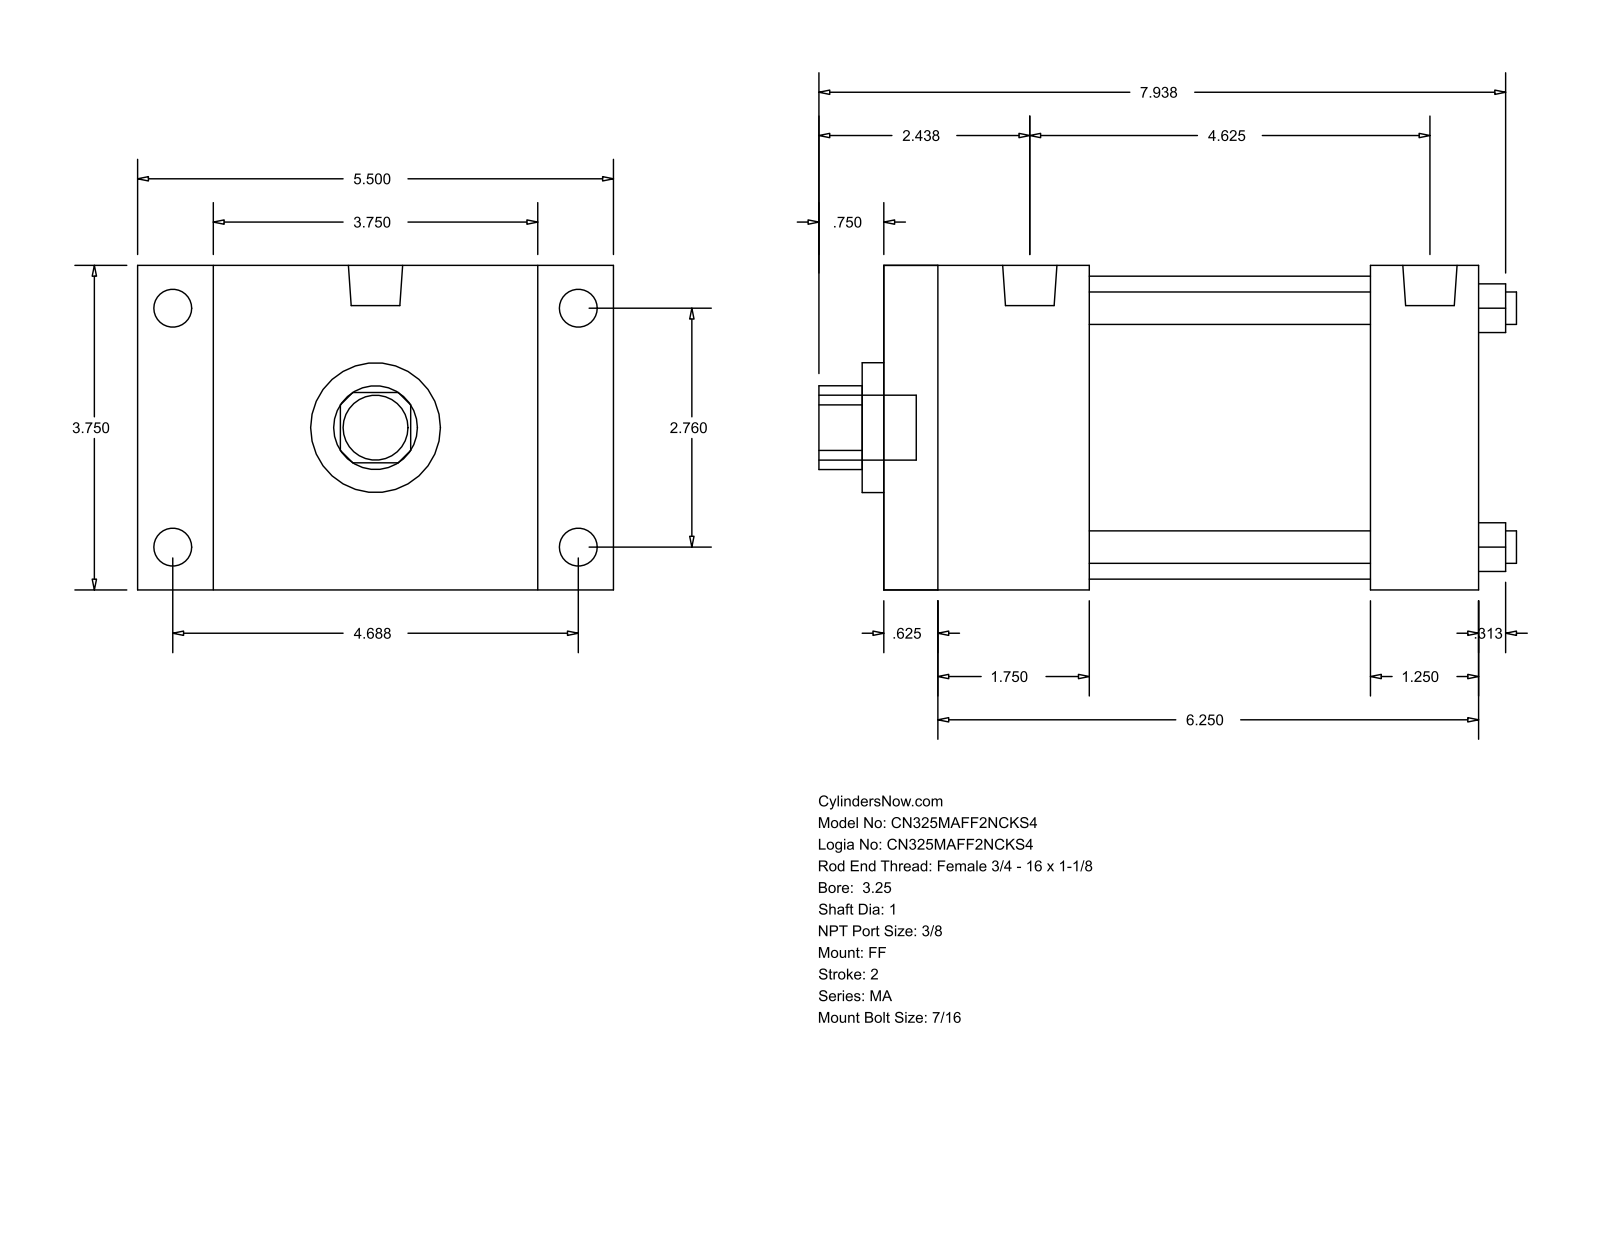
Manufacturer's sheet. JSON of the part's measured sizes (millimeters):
{"part_name": "MA_FF__0325_1", "step_written_by": "GSSL Pune (CONFIG_CONTROL_DESIGN)", "units": "millimeters", "bodies": {"solids": 0, "faces": 92, "planar": 64, "cylindrical": 28, "other": 0}, "overall_size": [204.79, 139.7, 95.25], "round_holes": [[9.53, 4], [25.4, 1], [38.1, 1], [88.9, 1]], "round_bosses_or_shafts": [[11.11, 8], [15.93, 2], [19.05, 1]], "partial_cylinders_radius": [[12.29, 1]], "face_to_face_distances": [95.24, 174.63, 15.87, 158.76, 22.23, 117.47, 60.33, 142.88, 44.46, 127.01], "hole_center_spacings": [49.57, 70.1, 99.14]}
